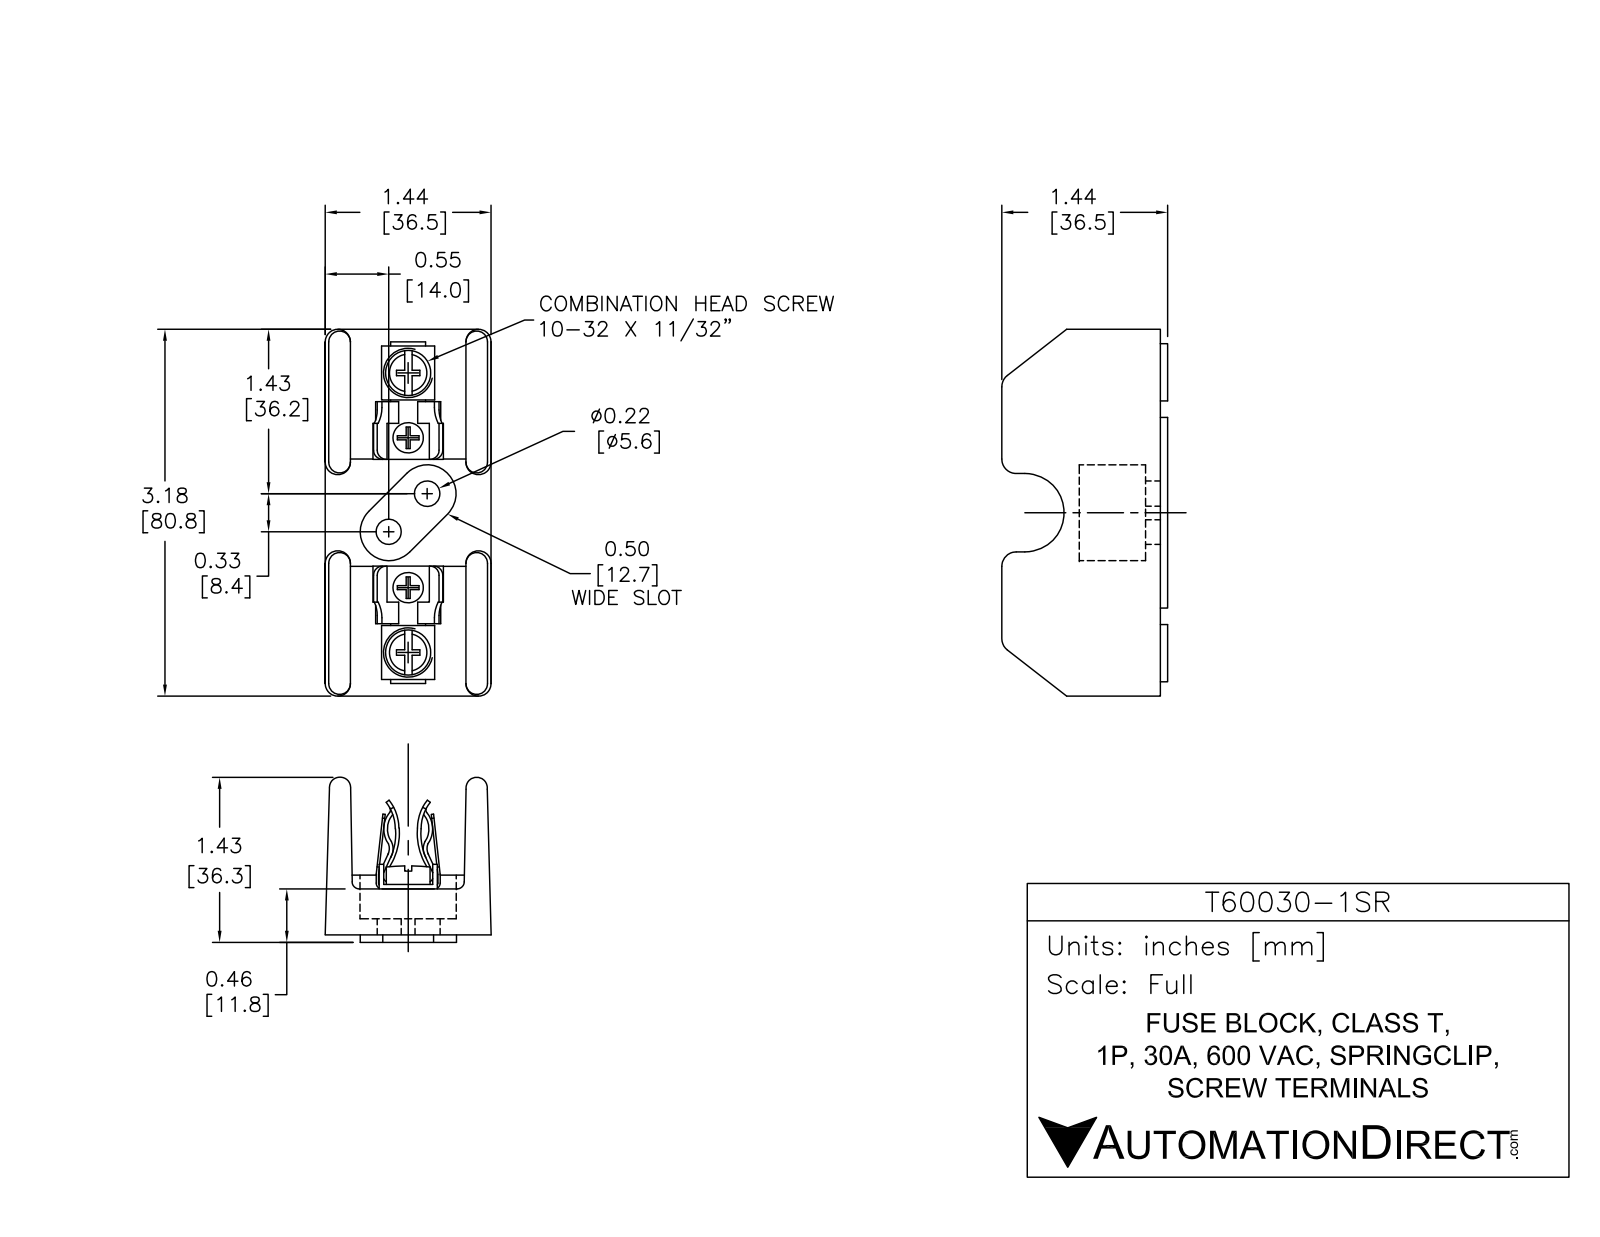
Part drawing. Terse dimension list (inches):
name: T60030-1SR
written by: SolidWorks 2019 (AUTOMOTIVE_DESIGN)
unit: in
bodies: 5 solids, 234 faces (100 planar, 102 cylindrical, 32 other)
size: 3.181 × 1.437 × 1.437
volume: 3.219 in³; area: 32.38 in²
holes: 2× ⌀0.22, 2× ⌀0.22
bosses: 2× ⌀0.472, 2× ⌀0.375
rounds: 22× R0.125, 8× R0.25, 4× R0.2, 2× R0.21, 2× R0.329, 1× R0.244, 1× R0.294
face distances: 0.25, 1.187, 0.421, 1.437, 0.937, 0.5, 0.05, 0.079, 0.55, 0.471
hole spacings: 1.067, 1.394, 0.468, 2.438
